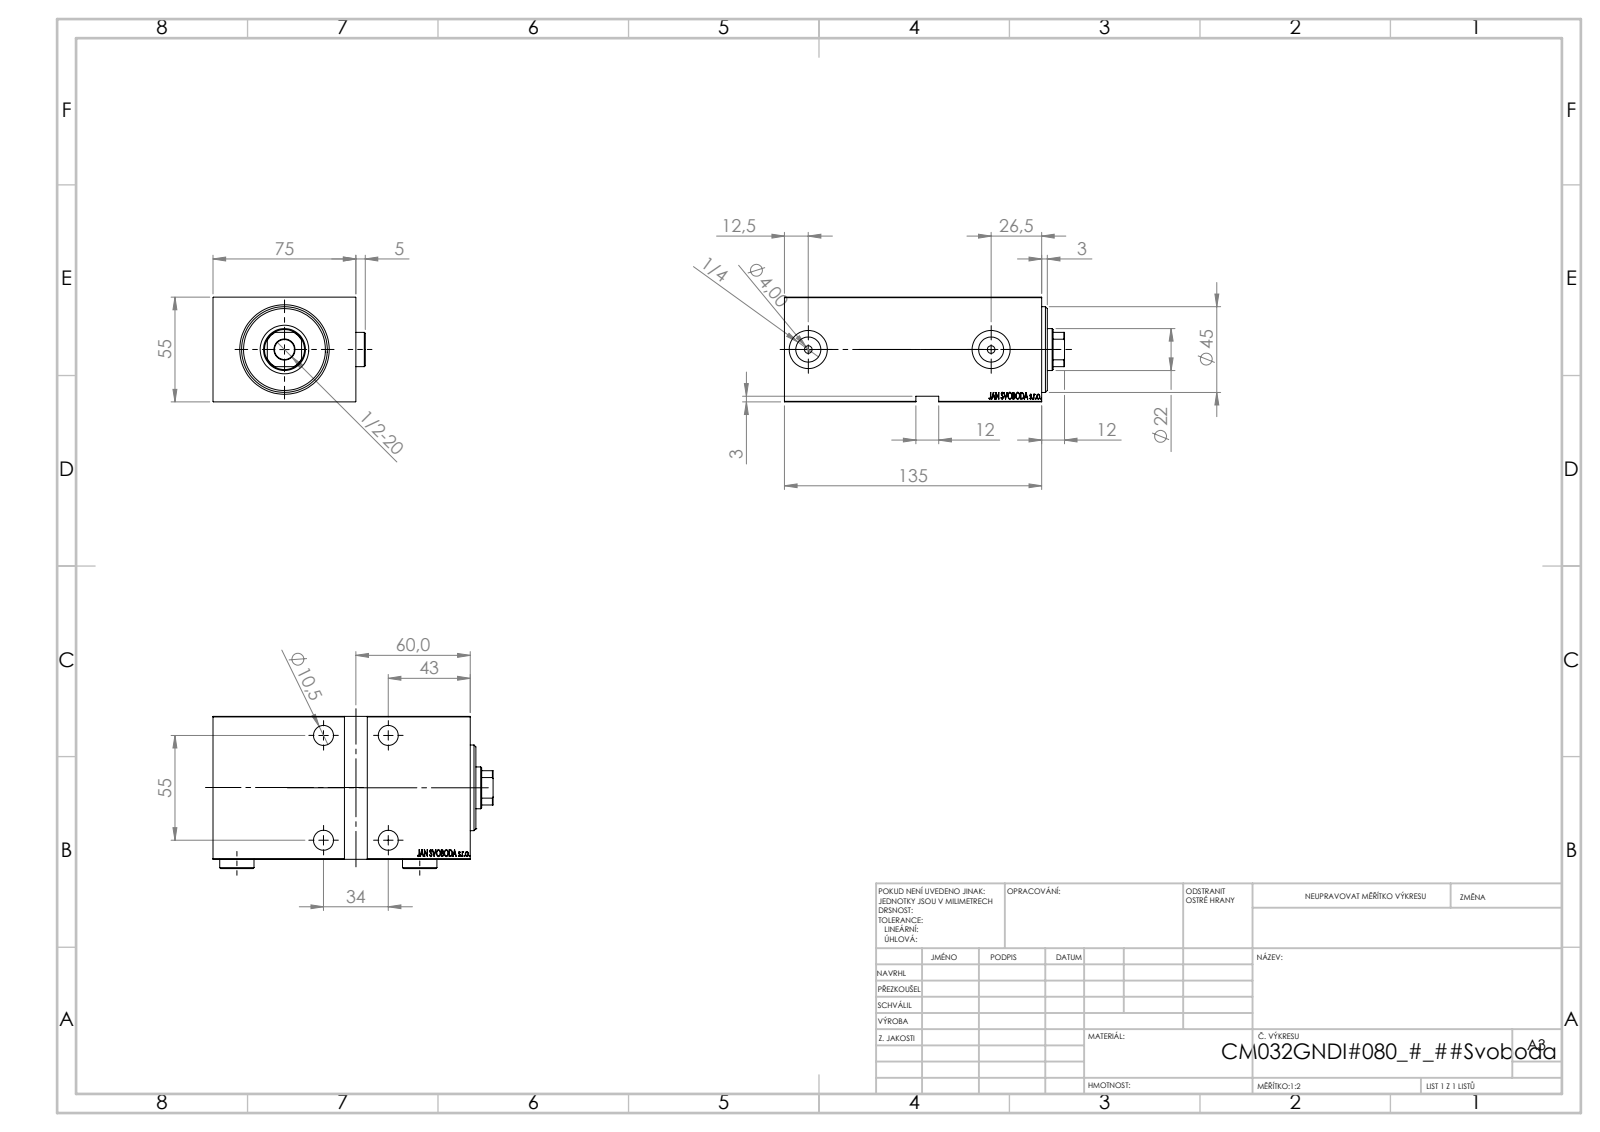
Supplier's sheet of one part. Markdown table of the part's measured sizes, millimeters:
| quantity | value |
| --- | --- |
| part name | Zatka_OIL_PORT; V450CM_G_VCP; V450CM_G_Body; V450CM_VC_G |
| STEP written by | SolidWorks 2019 (CONFIG_CONTROL_DESIGN) |
| units | millimeters |
| bodies | 5 solids, 912 faces (446 planar, 68 cylindrical, 398 other) |
| overall size | 147 × 79.9 × 55 |
| volume | 491 329 mm³ |
| surface area | 86 215 mm² |
| round holes (diameter × count) | 10.5 × 5, 16.5 × 4, 4 × 2, 13.16 × 2, 20 × 2, 22 × 1, 25.5 × 1, 32 × 1, 34 × 1, 45 × 1 |
| round bosses / shafts (diameter × count) | 18 × 2, 27 × 1 |
| partial cylindrical surfaces (radius × count) | 10.5 × 1 |
| main face-to-face distances | 55, 75, 135, 5, 3, 130, 10, 120, 125, 74.9 |
| hole center spacings | 34, 55, 64.66, 96 |
